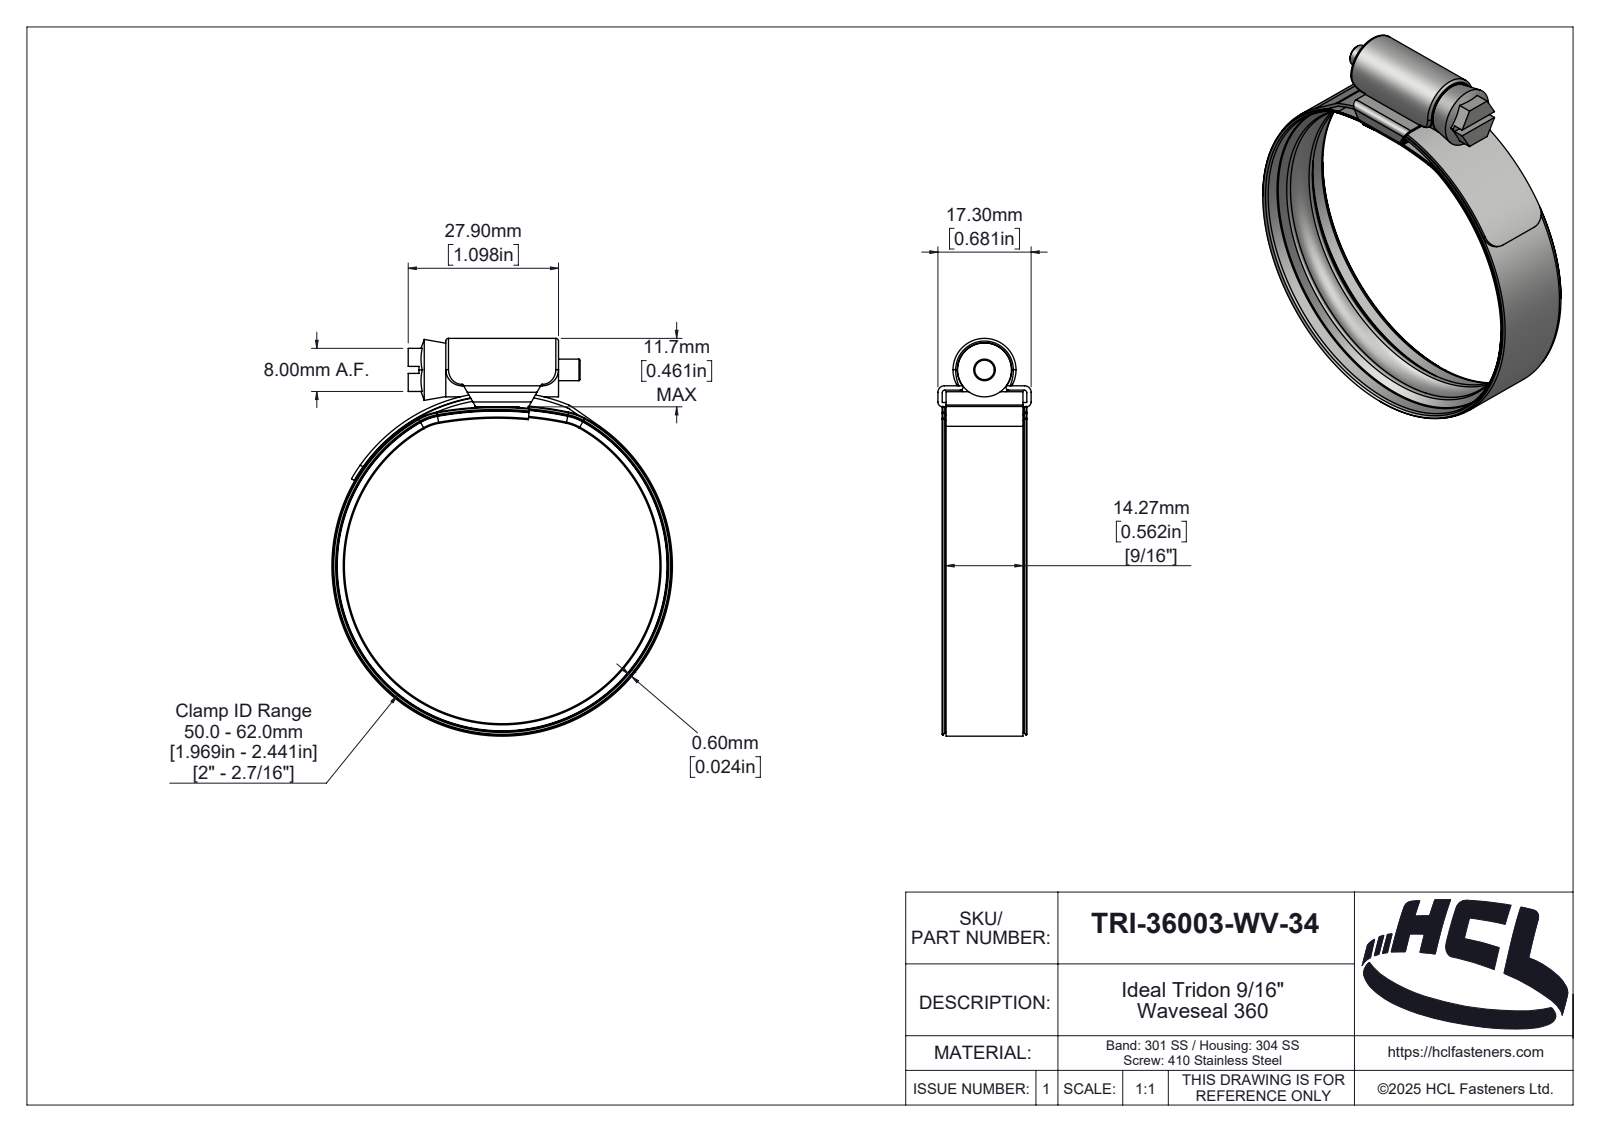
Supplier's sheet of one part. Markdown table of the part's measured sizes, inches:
| quantity | value |
| --- | --- |
| part name | TRI-36003-WV-34 |
| STEP written by | SolidWorks 2025 (AUTOMOTIVE_DESIGN) |
| units | inches |
| bodies | 4 solids, 418 faces (42 planar, 119 cylindrical, 257 other) |
| overall size | 2.906 × 2.488 × 0.681 |
| volume | 0.337 in³ |
| surface area | 26.08 in² |
| round holes (diameter × count) | 2.417 × 1, 2.441 × 1 |
| round bosses / shafts (diameter × count) | 2.488 × 1, 2.433 × 1, 0.394 × 1, 0.157 × 1 |
| partial cylindrical surfaces (radius × count) | 0.02 × 6, 0.118 × 4, 0.004 × 2, 0.035 × 2, 0.047 × 2, 0.39 × 2, 0.398 × 2, 0.018 × 1 |
| main face-to-face distances | 0.031, 0.122, 0.561, 0.091, 0.024, 0.154, 1.098, 0.06, 0.621, 0.65 |
